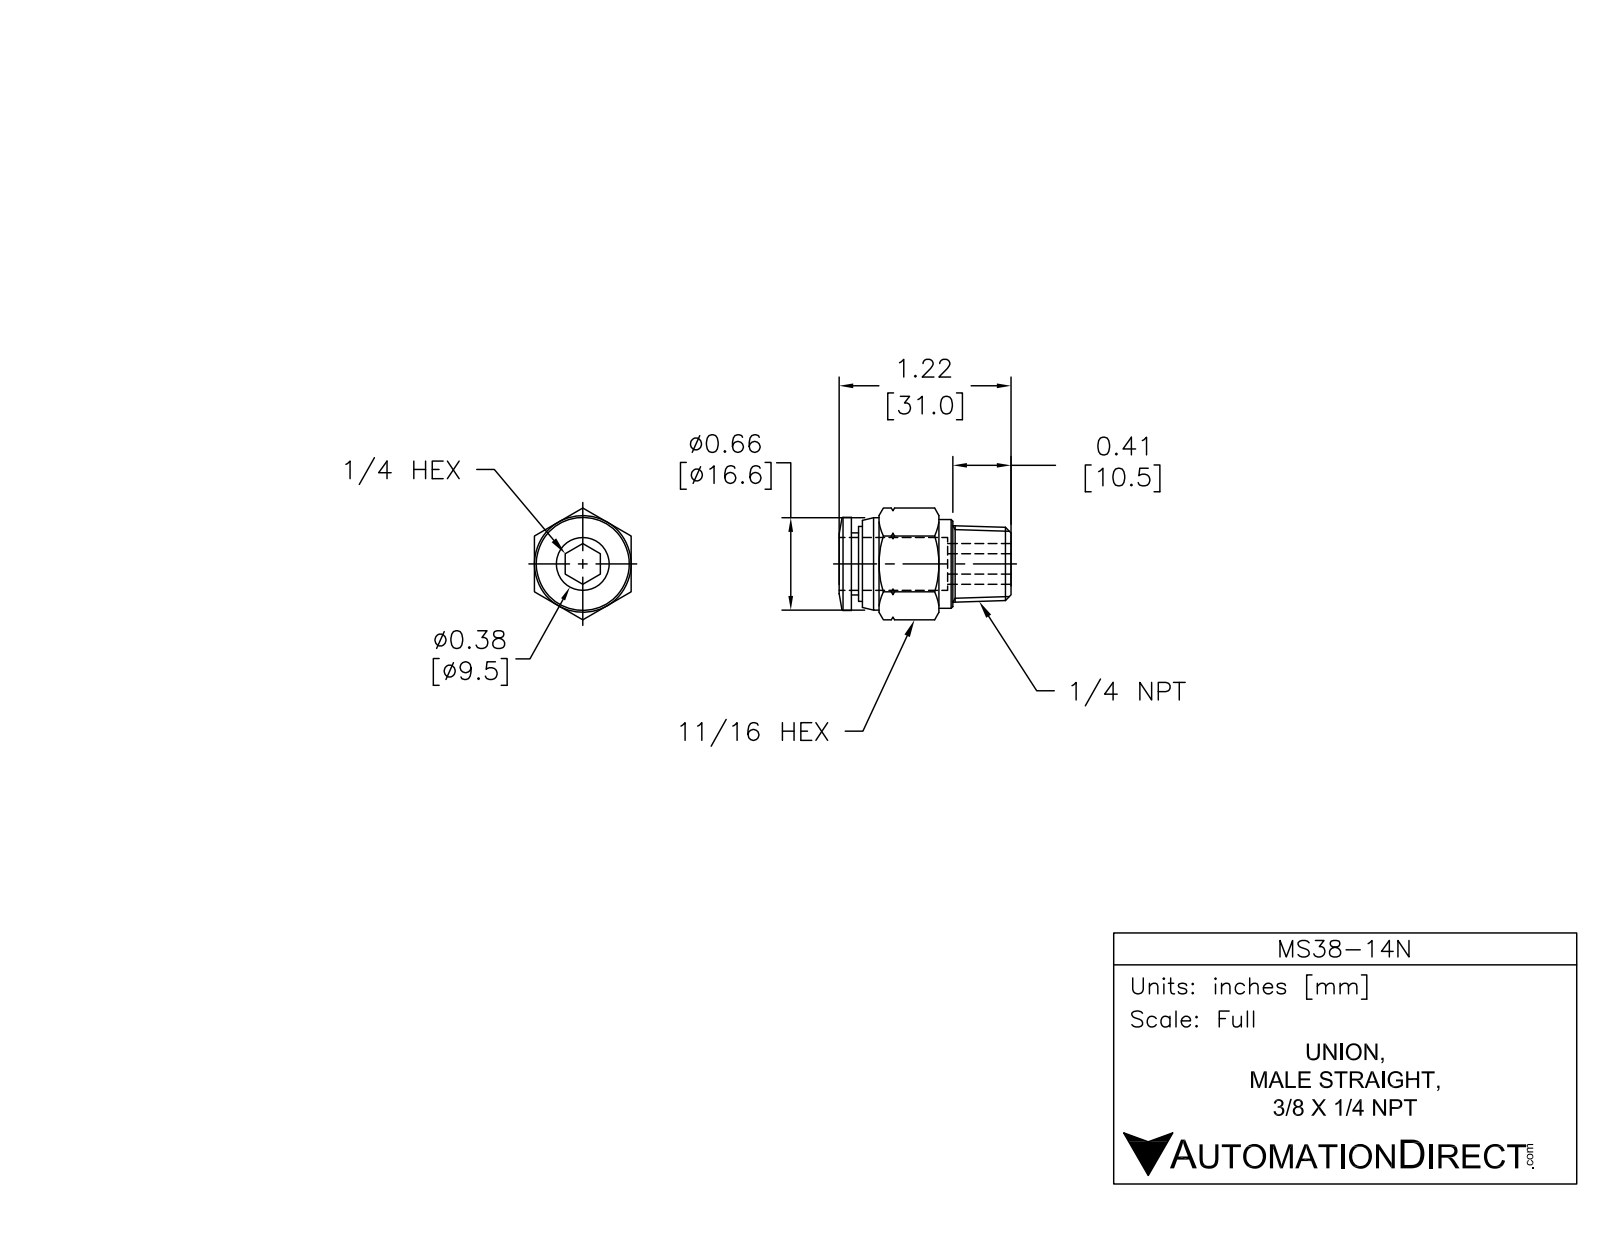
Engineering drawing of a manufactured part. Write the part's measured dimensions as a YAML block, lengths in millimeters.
part_name: "PC3-8--N02"
step_written_by: "Autodesk Inventor 2008 (AUTOMOTIVE_DESIGN)"
units: millimeters
bodies: {solids: 1, faces: 53, planar: 14, cylindrical: 7, other: 32}
overall_size: [31, 20.16, 17.46]
volume: 4275
surface_area: 2984
round_holes:
  - {diameter: 6.4, count: 1}
  - {diameter: 9.8, count: 1}
round_bosses_or_shafts:
  - {diameter: 16.8, count: 1}
  - {diameter: 16.65, count: 1}
  - {diameter: 16, count: 1}
  - {diameter: 13.5, count: 1}
  - {diameter: 11.2, count: 1}
face_to_face_distances: [17.46, 28.8, 26.8, 2, 27.5, 0.7, 1.3, 11.4, 15.4, 16.1]
